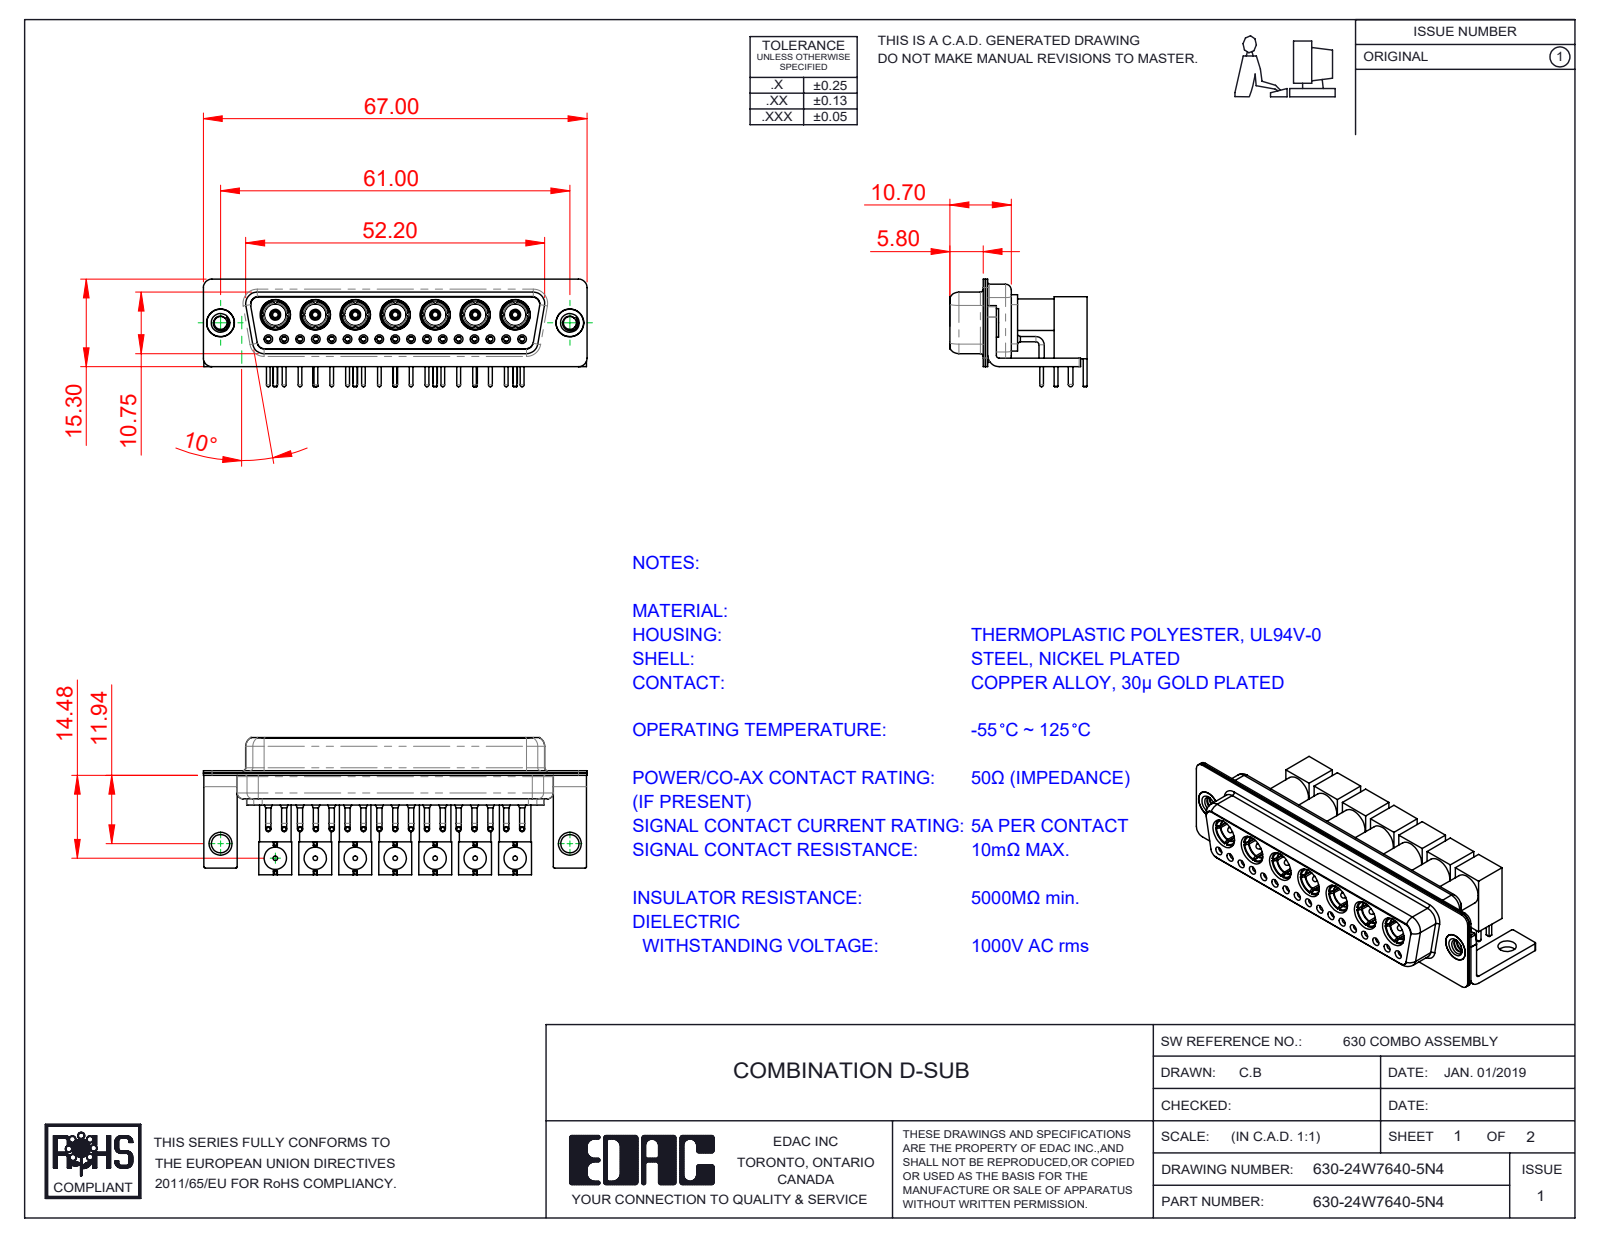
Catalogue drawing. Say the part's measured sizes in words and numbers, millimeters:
The part is named "Co-Ax Plug Assy_RA 50; 630Combo Threaded Rivet_3; 630-24W7640-5N4; 630Combo Housing_24W7 (+8 more)". Its 3-D file was written by "SolidWorks 2020 (CONFIG_CONTROL_DESIGN)". It is 66 solids with 2396 faces: 811 planar, 1001 cylindrical and 584 other. Overall it measures 67 by 23.95 by 18.8 millimeters. Its volume is 9 443 cubic millimeters and its surface area 21 048 square millimeters. Round holes: 24 of diameter 1.1, 24 of diameter 1.5, 17 of diameter 0.9, 17 of diameter 1.6, 17 of diameter 2, 9 of diameter 4.85, 7 of diameter 0.8, 7 of diameter 2.83, 7 of diameter 3.1, 7 of diameter 3.3, 7 of diameter 3.9, 7 of diameter 3.92. Round bosses or shafts: 17 of diameter 0.9, 17 of diameter 0.65, 9 of diameter 5, 7 of diameter 5.5, 7 of diameter 5.2, 7 of diameter 4.75, 7 of diameter 4.15, 7 of diameter 4. Partial cylindrical surfaces (rounded edges, fillets, slot ends): 16 of radius 0.25, 16 of radius 1.5, 13 of radius 2, 12 of radius 1.35, 8 of radius 1.6, 7 of radius 2.1, 5 of radius 0.5, 4 of radius 0.6. The main face-to-face distances are 0.4, 6.98, 13.96, 0.8, 20.94, 17.75, 1.8, 1.22, 5.76, 5.75. The hole center spacings are 2.77, 5.54, 8.31, 11.08, 6.98, 13.85, 16.62, 13.96.
